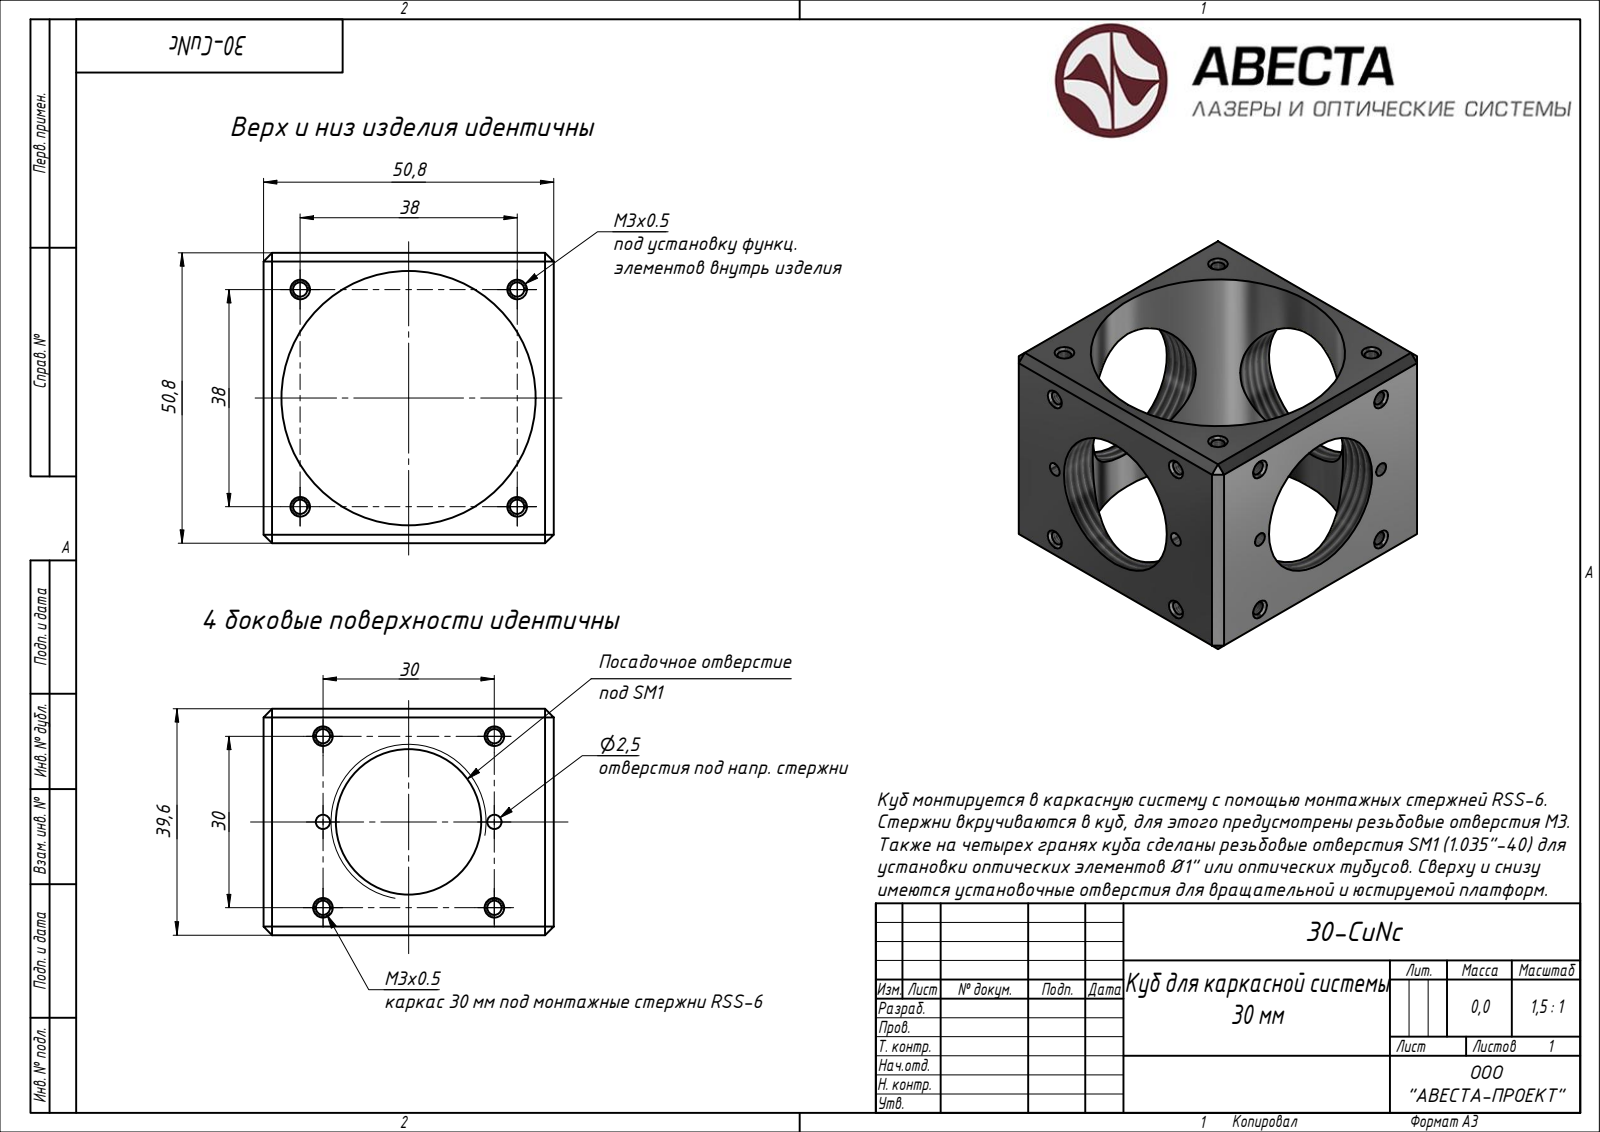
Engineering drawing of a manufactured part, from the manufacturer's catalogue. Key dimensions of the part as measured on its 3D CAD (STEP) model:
Part name (STEP PRODUCT): 30-Cu1
STEP written by: Autodesk Inventor 2020 (AUTOMOTIVE_DESIGN)
Units: millimetres
Bodies: 1 solid, 119 faces (58 planar, 37 cylindrical, 24 other)
Overall size (bounding box): 50.8 × 50.8 × 39.6
Volume: 30 679 mm³ · Surface area: 14 031 mm²
Round holes (diameter × count): ⌀2.46 ×12, ⌀2.5 ×4, ⌀25.48 ×2, ⌀44.5 ×1
Main face-to-face distances: 50.8, 39.6, 61.79, 69.72, 6, 44.8, 38.8, 33.6, 27.6, 78.01
Hole centre spacings: 15, 30, 21.21, 33.54, 26.87, 38, 42.43, 53.74
